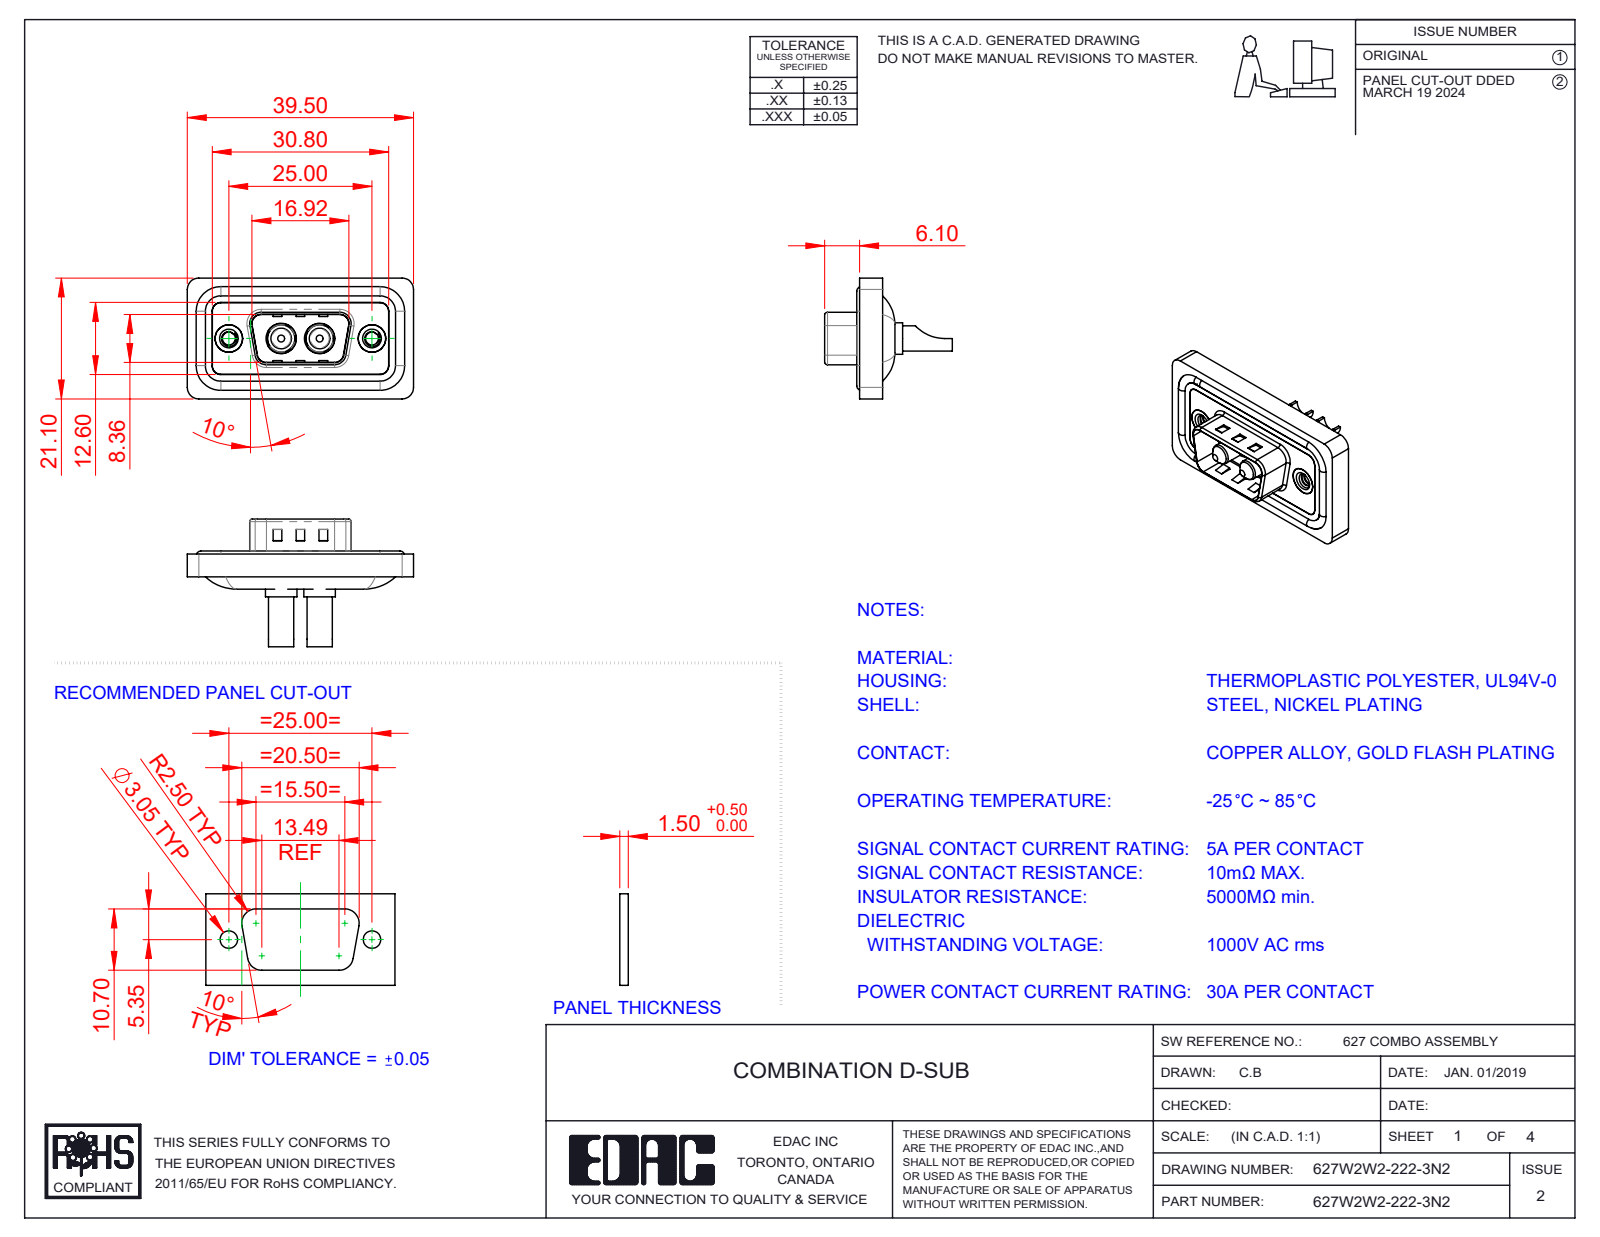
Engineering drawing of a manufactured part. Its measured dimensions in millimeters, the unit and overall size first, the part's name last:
Units: millimetres
Overall size (bounding box): 39.5 × 22.3 × 21.1
Round holes (diameter × count): ⌀2.26 ×2, ⌀3.5 ×2, ⌀4 ×2, ⌀4.8 ×2, ⌀4.85 ×2, ⌀5 ×2, ⌀5.3 ×2
Round bosses / shafts (diameter × count): ⌀1.6 ×4, ⌀5.5 ×2, ⌀5.2 ×2, ⌀4.9 ×2, ⌀4.75 ×2, ⌀4.4 ×2, ⌀3.75 ×2, ⌀3.6 ×2
Partial cylindrical surfaces — rounded edges, fillets, slot ends (radius × count): R1.5 ×22, R2 ×18, R0.5 ×8, R1.6 ×8, R0.25 ×4, R0.6 ×4, R0.65 ×4, R0.9 ×4
Main face-to-face distances: 0.4, 1.1, 2.9, 3.1, 0.5, 1.6, 1.5, 2.5, 4, 0.7
Hole centre spacings: 9.14, 15.86, 6.72, 25
Volume: 4 509 mm³ · Surface area: 7 199 mm²
Bodies: 11 solids, 501 faces (171 planar, 224 cylindrical, 106 other)
Part name (STEP PRODUCT): 627Combo Waterproof Housing_09 Contacts; 627Combo Shell Rear_09 Contacts; 627W2W2-222-3N2; 627Combo Threaded Rivet_2 (+3 more)
STEP written by: SolidWorks 2023 (CONFIG_CONTROL_DESIGN)
